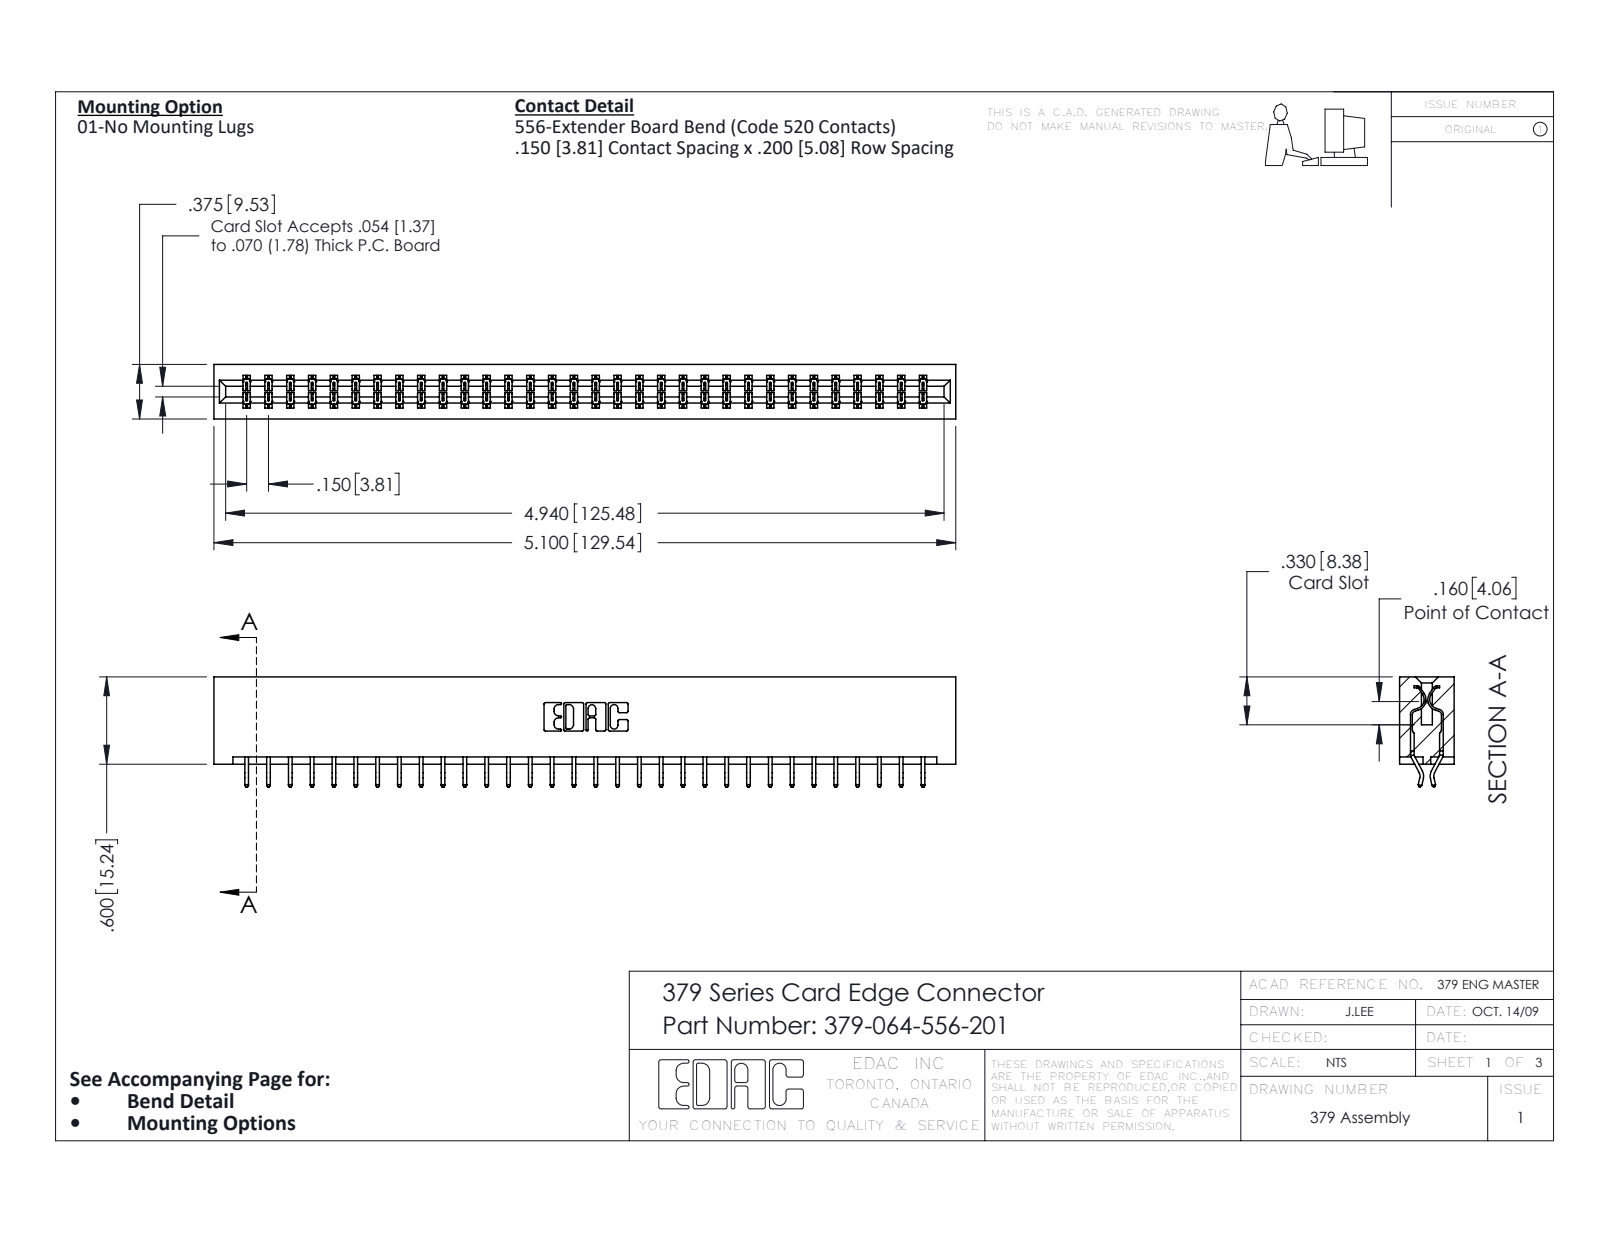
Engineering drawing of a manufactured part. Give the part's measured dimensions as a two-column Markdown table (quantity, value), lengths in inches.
| quantity | value |
| --- | --- |
| part name | 379 Part_Lugless; 345-292-001_556 Tail; 379-064-556-201 |
| STEP written by | SolidWorks 2016 (CONFIG_CONTROL_DESIGN) |
| units | inches |
| bodies | 65 solids, 3818 faces (2626 planar, 1192 cylindrical, 0 other) |
| overall size | 5.1 × 0.757 × 0.375 |
| volume | 0.88 in³ |
| surface area | 24.92 in² |
| partial cylindrical surfaces (radius × count) | 0.006 × 96, 0.01 × 22, 0.007 × 6, 0.031 × 6, 0.026 × 3, 0.01 × 2, 0.014 × 2, 0.022 × 2 |
| main face-to-face distances | 0.3, 0.075, 0.375, 0.225, 0.6, 0.15, 0.076, 0.15, 0.025, 0.1 |
